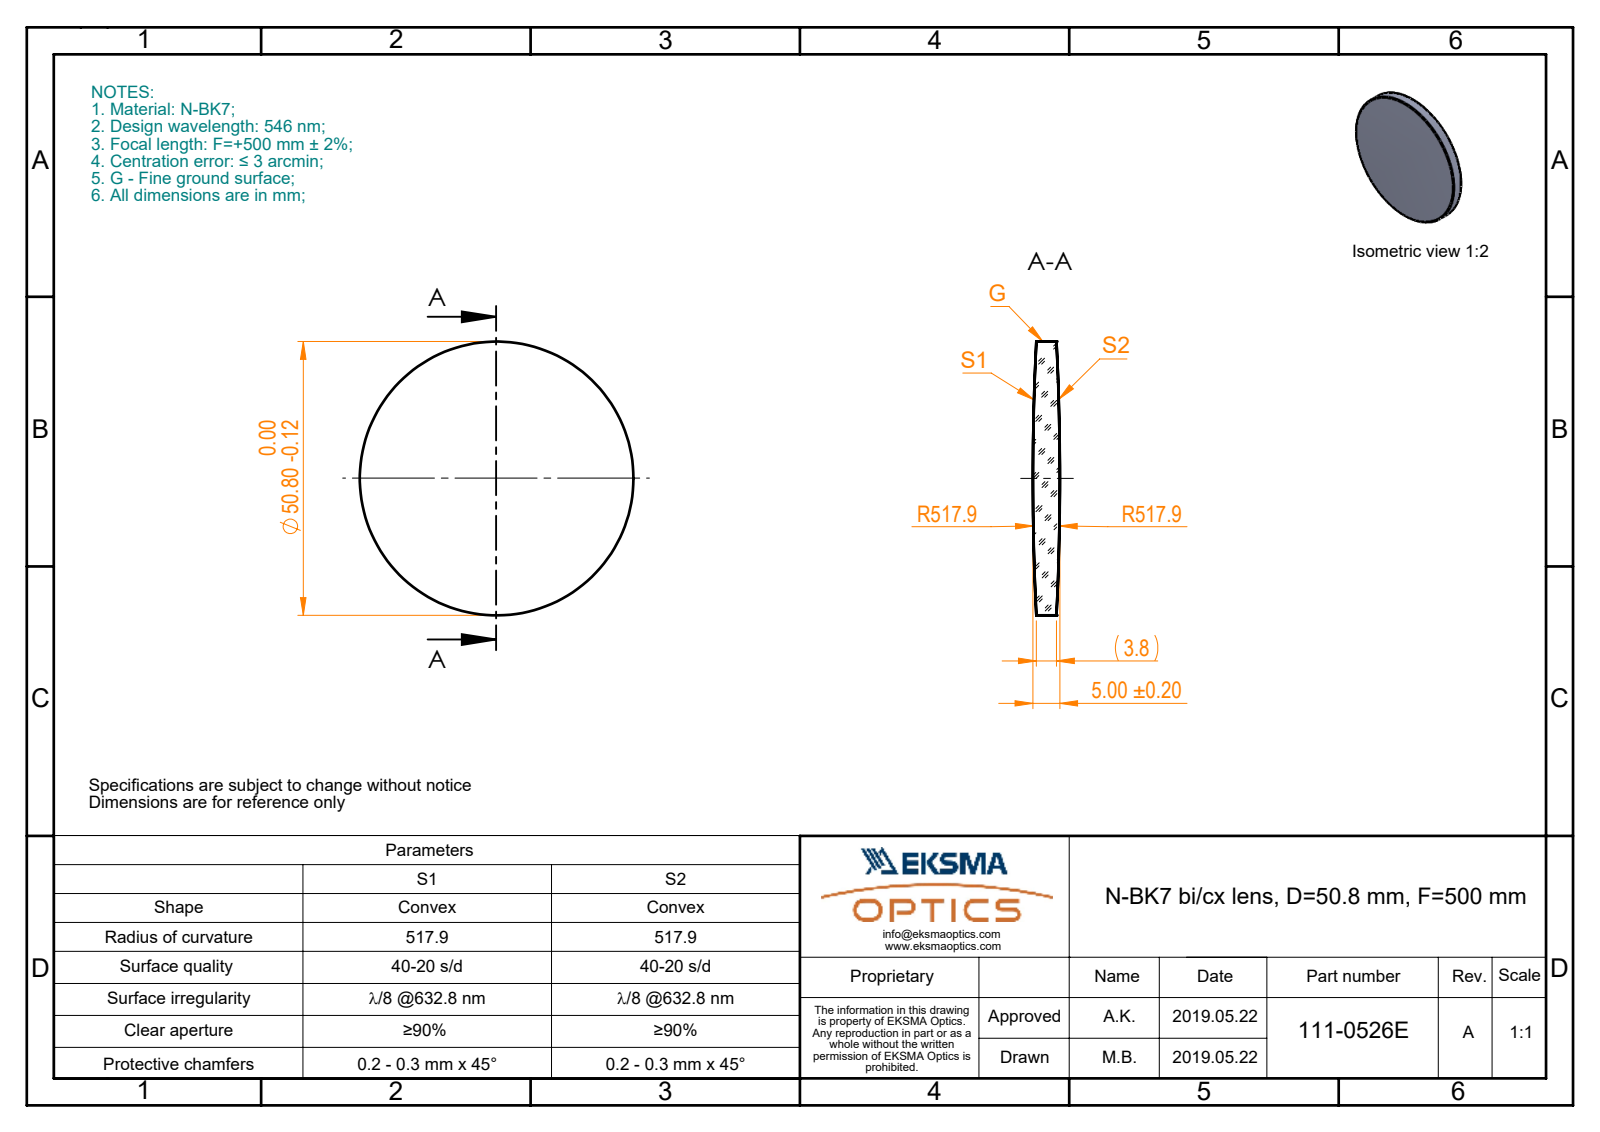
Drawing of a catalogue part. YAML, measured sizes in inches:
part_name: "111-0526E BK7 bi-cx 50.8 F500"
step_written_by: "SolidWorks 2017 (CONFIG_CONTROL_DESIGN)"
units: inches
bodies: {solids: 1, faces: 6, planar: 0, cylindrical: 2, other: 4}
overall_size: [2, 2, 0.197]
volume: 0.541
surface_area: 7.215
round_bosses_or_shafts:
  - {diameter: 2, count: 1}
